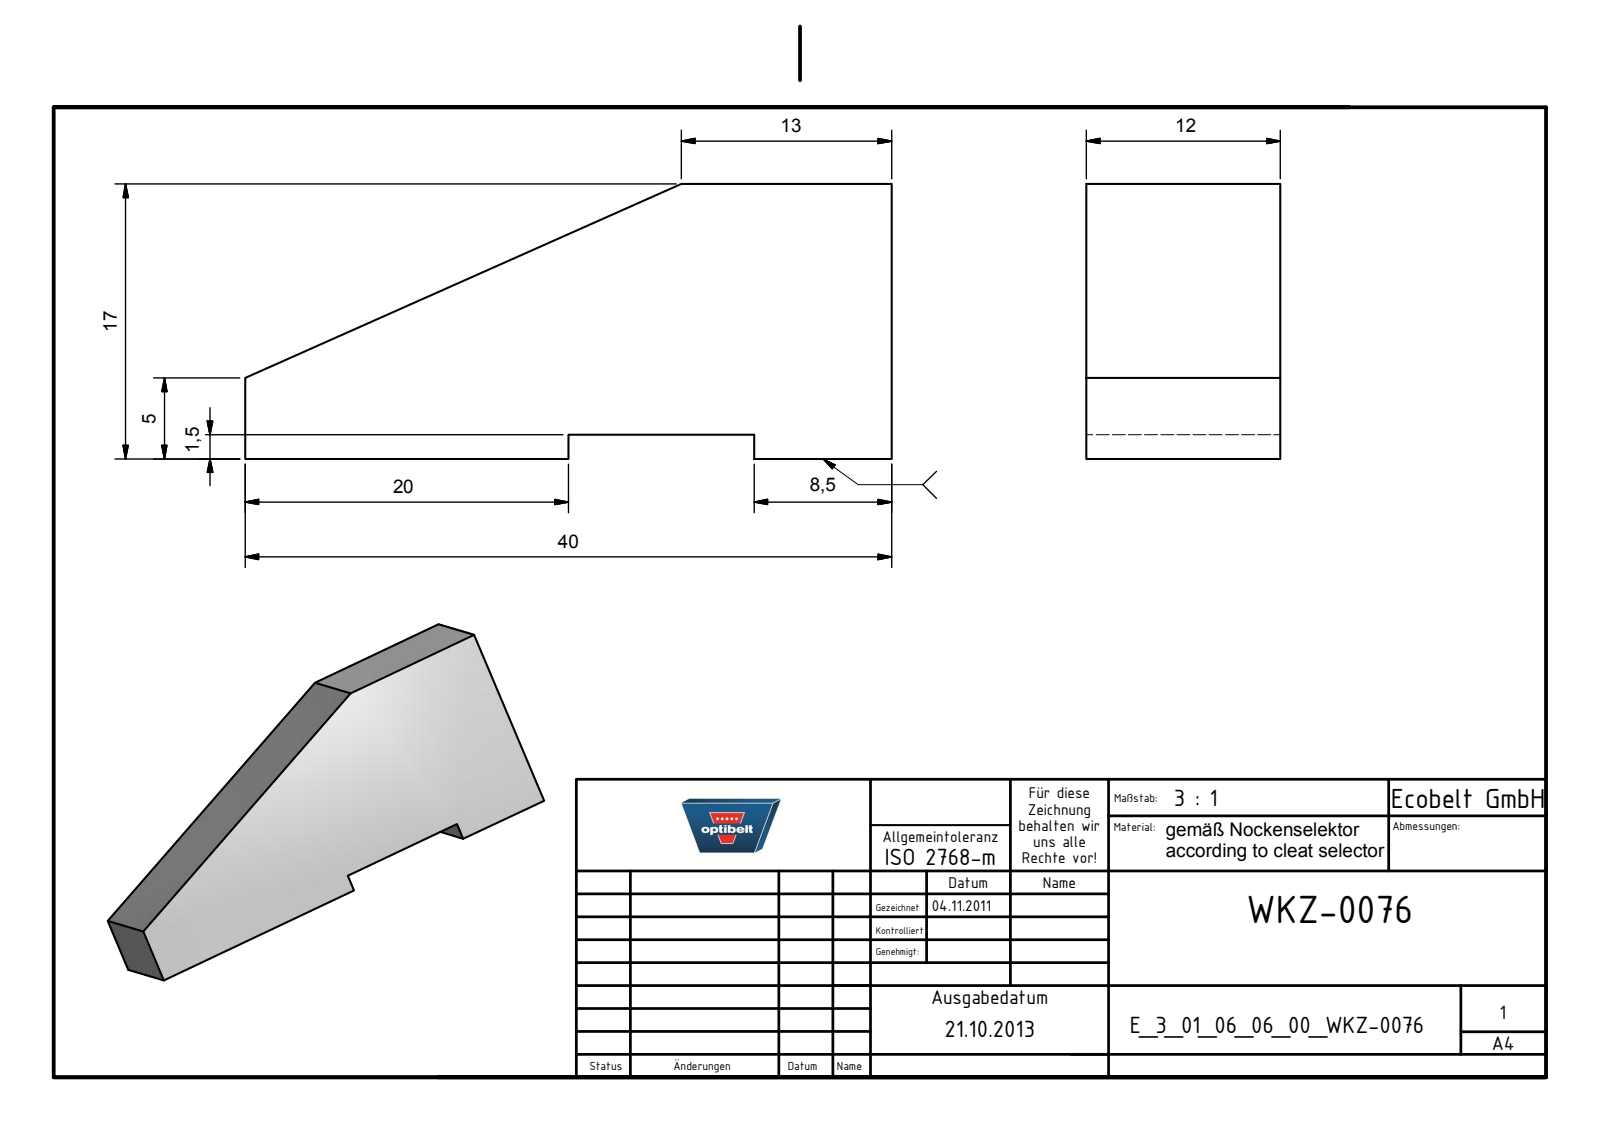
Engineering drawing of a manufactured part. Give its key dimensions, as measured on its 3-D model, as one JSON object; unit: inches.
{"part_name": "E_3_01_06_06_00_WKZ-0076", "step_written_by": "Autodesk Inventor 2025 (AUTOMOTIVE_DESIGN)", "units": "inches", "bodies": {"solids": 1, "faces": 11, "planar": 11, "cylindrical": 0, "other": 0}, "overall_size": [1.575, 0.669, 0.472], "volume_in3": 0.367, "surface_area_in2": 3.553, "face_to_face_distances": [0.472, 0.669, 0.059, 0.61, 1.575, 0.787, 1.24, 0.335, 0.453]}
